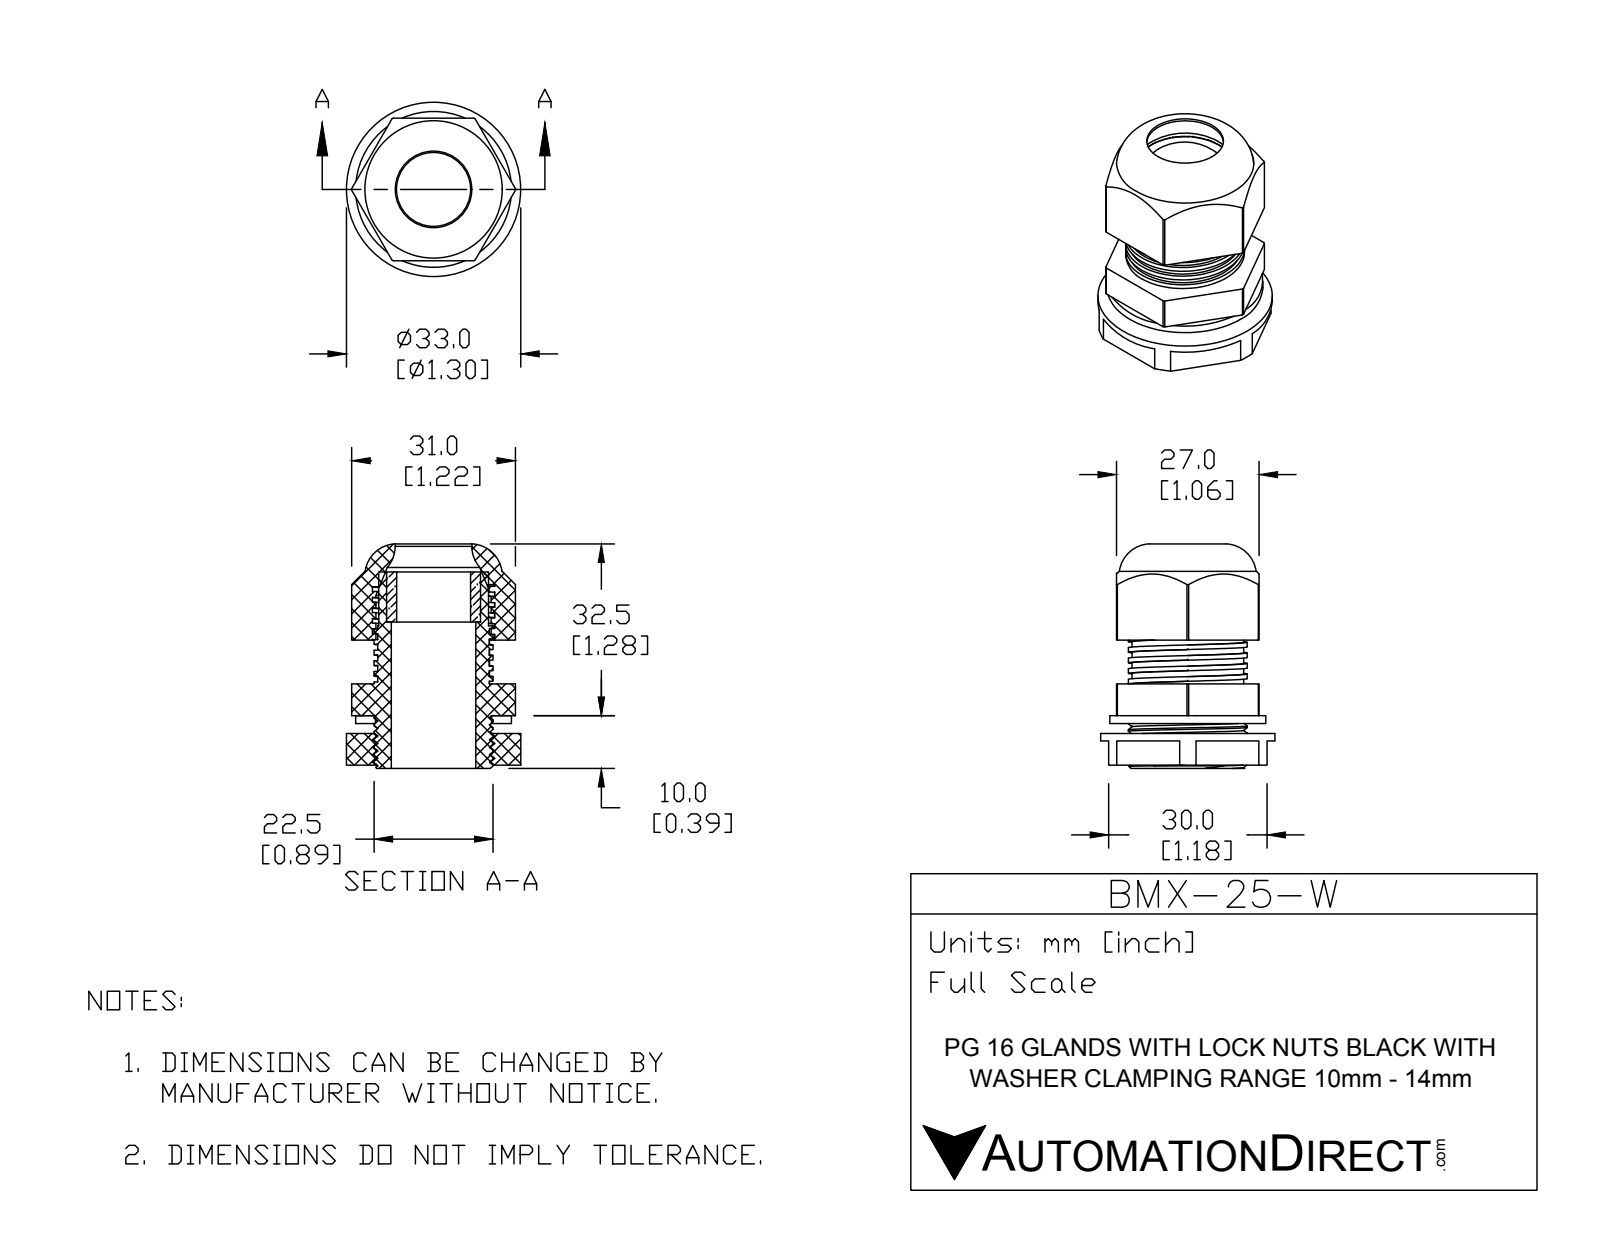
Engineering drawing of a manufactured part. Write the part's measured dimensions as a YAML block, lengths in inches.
part_name: "BMX-25-W"
step_written_by: "SolidWorks 2015 (CONFIG_CONTROL_DESIGN)"
units: inches
bodies: {solids: 5, faces: 204, planar: 98, cylindrical: 82, other: 24}
overall_size: [1.673, 1.299, 1.299]
volume: 0.936
surface_area: 22.54
round_holes:
  - {diameter: 0.551, count: 1}
  - {diameter: 0.571, count: 1}
  - {diameter: 0.63, count: 1}
  - {diameter: 0.701, count: 1}
  - {diameter: 0.859, count: 1}
  - {diameter: 0.866, count: 1}
  - {diameter: 1.024, count: 1}
round_bosses_or_shafts:
  - {diameter: 1.299, count: 1}
  - {diameter: 1.161, count: 1}
  - {diameter: 0.886, count: 1}
  - {diameter: 0.819, count: 1}
partial_cylinders:
  - {radius: 0.61, count: 1}
face_to_face_distances: [0.059, 1.063, 0.335, 0.236, 0.098, 0.295, 1.122, 0.276, 0.039, 0.571]
